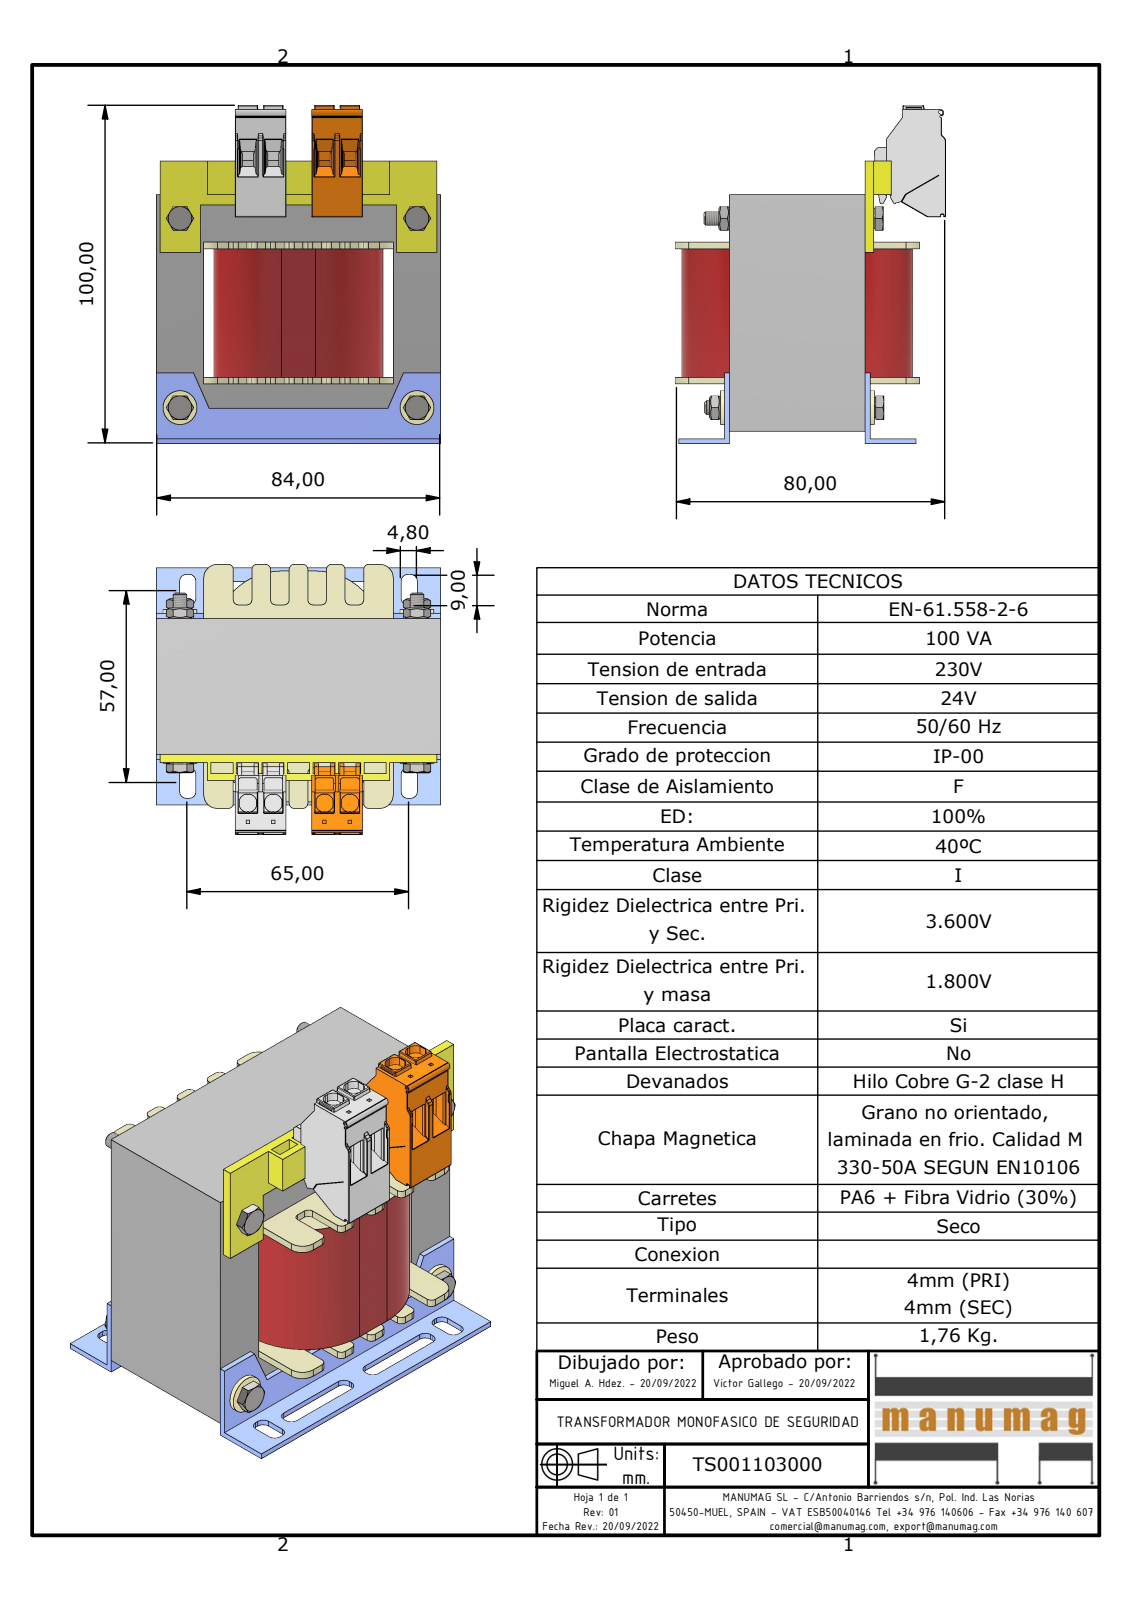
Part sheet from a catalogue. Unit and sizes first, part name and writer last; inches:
Units: inches
Overall size (bounding box): 3.945 × 3.307 × 3.138
Round holes (diameter × count): ⌀0.128 ×4, ⌀0.157 ×4, ⌀0.177 ×4
Round bosses / shafts (diameter × count): ⌀0.232 ×4, ⌀0.143 ×4, ⌀0.394 ×2, ⌀0.193 ×2
Partial cylindrical surfaces — rounded edges, fillets, slot ends (radius × count): R0.006 ×160, R0.008 ×48, R0.079 ×40, R0.059 ×32, R0.02 ×12, R0.012 ×7, R0.039 ×4, R0.106 ×4
Main face-to-face distances: 0.551, 2.205, 1.102, 1.575, 1.654, 2.756, 0.059, 2.126, 3.307, 0.079
Hole centre spacings: 2.205, 2.756, 3.529
Volume: 17.83 in³ · Surface area: 132.1 in²
Bodies: 19 solids, 3765 faces (3011 planar, 516 cylindrical, 238 other)
Part name (STEP PRODUCT): TS001103000; EI84 x 70 - 40 (RC28); EI84; AF28DIN (+6 more)
STEP written by: Autodesk Inventor 2023 (AUTOMOTIVE_DESIGN)
